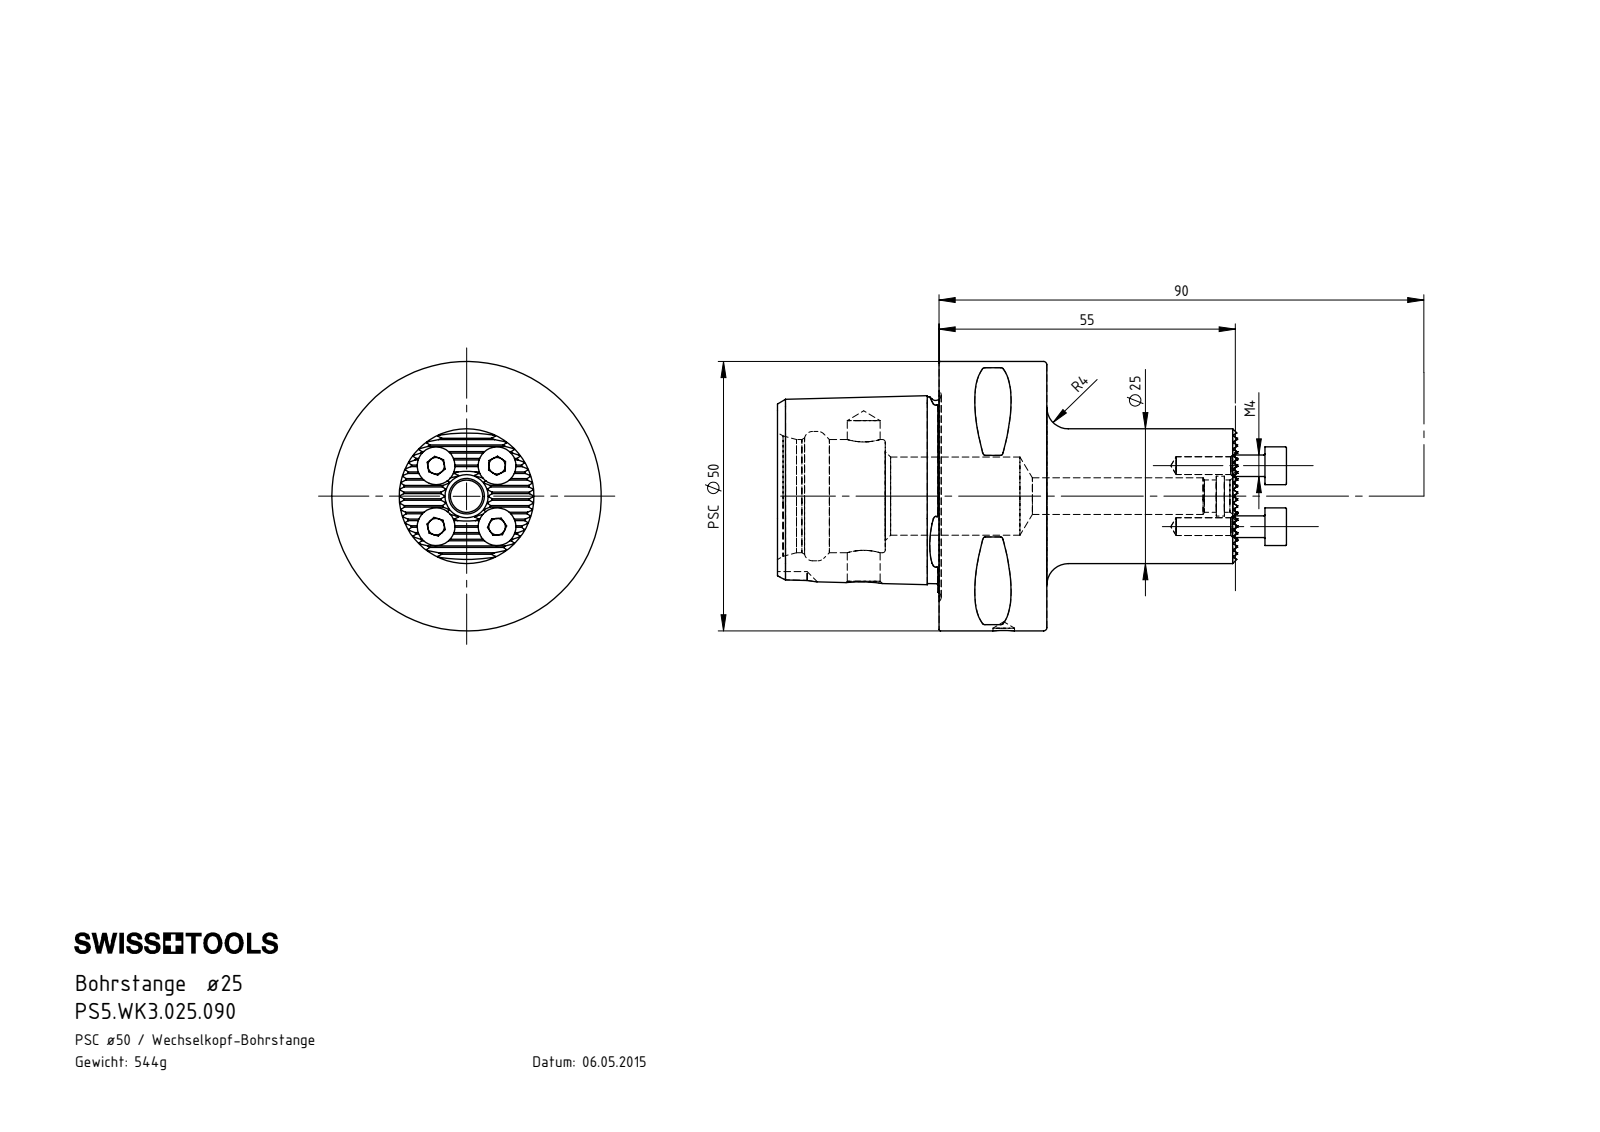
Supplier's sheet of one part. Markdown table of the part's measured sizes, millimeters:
| quantity | value |
| --- | --- |
| part name | PS5.WK3.025.090; DIN 3771 - 6x1; ISO 4762 - M4 x 12; PS5-WK3.025.090_B |
| STEP written by | SolidWorks 2017 (AUTOMOTIVE_DESIGN) |
| units | millimeters |
| bodies | 6 solids, 448 faces (212 planar, 101 cylindrical, 135 other) |
| overall size | 94.5 × 50 × 50 |
| volume | 70 337 mm³ |
| surface area | 18 381 mm² |
| round holes (diameter × count) | 3.3 × 4, 4 × 1, 6 × 1, 6.1 × 1, 6.8 × 1, 7.4 × 1, 14.5 × 1, 21 × 1, 24 × 1 |
| round bosses / shafts (diameter × count) | 7 × 4, 4 × 4, 50 × 1, 25 × 1 |
| partial cylindrical surfaces (radius × count) | 0.12 × 19, 0.5 × 8, 4 × 1 |
| main face-to-face distances | 20, 30, 50, 4.33, 1.08, 3.25, 8.66, 5.41, 19.18, 7.58 |
| hole center spacings | 8, 11.32, 16.01, 26 |
